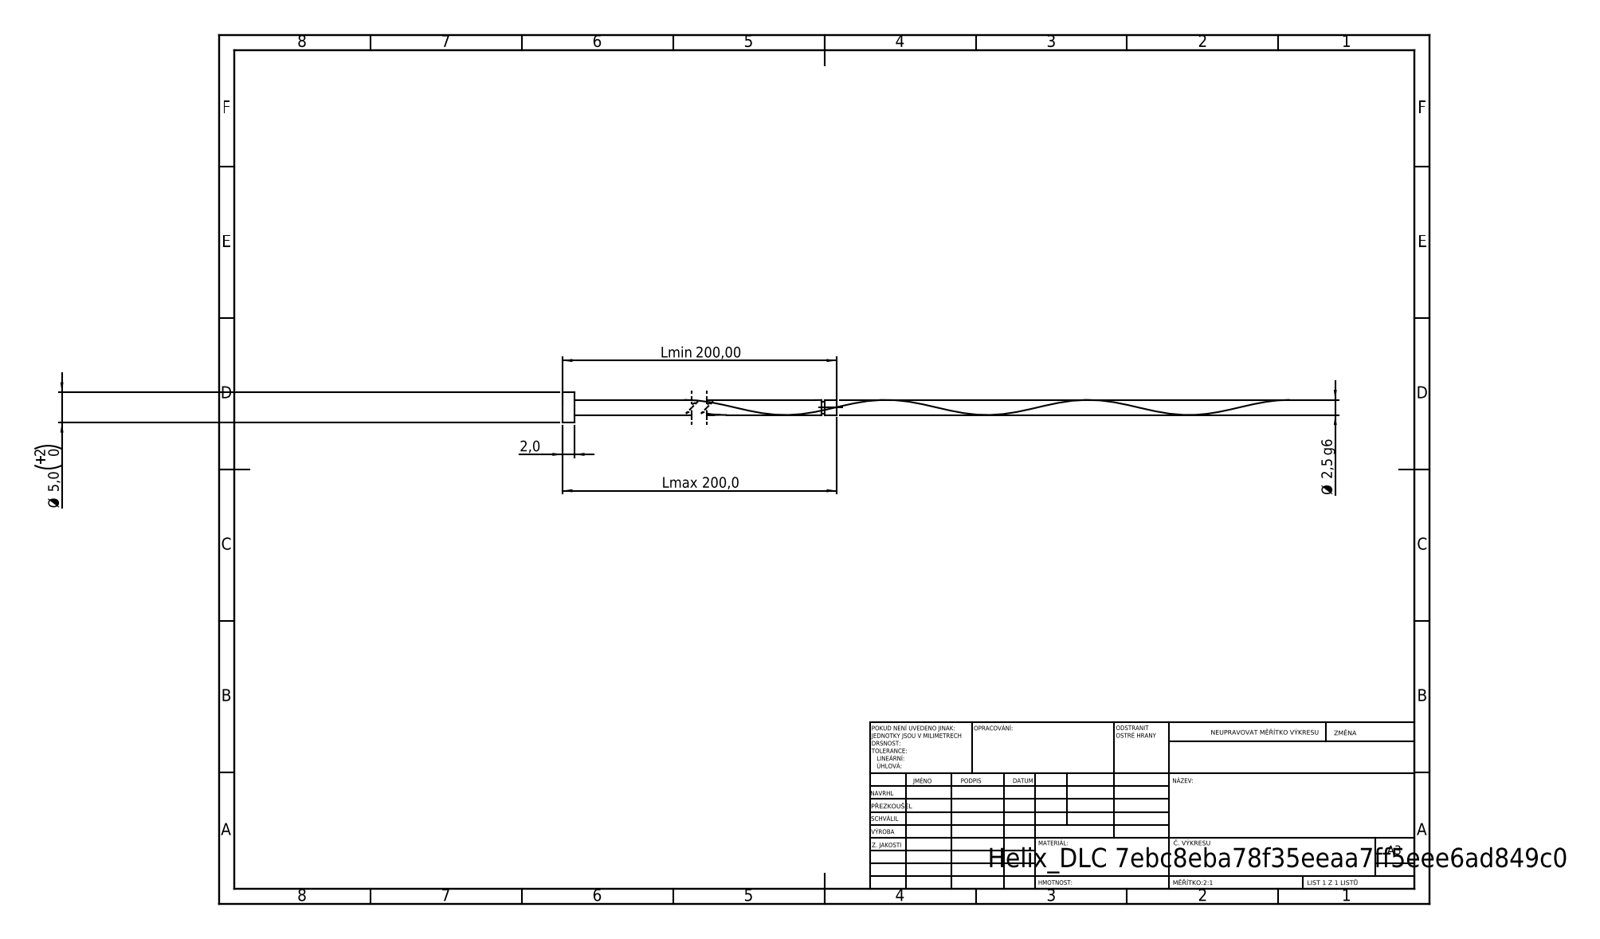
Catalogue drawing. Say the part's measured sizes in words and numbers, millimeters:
Its 3-D file was written by "SolidWorks 2019 (CONFIG_CONTROL_DESIGN)". It is 1 solid with 16 faces: 6 planar, 9 cylindrical and 1 other. Overall it measures 200 by 5 by 5 millimeters. Its volume is 1 219 cubic millimeters and its surface area 2 177 square millimeters. Round bosses or shafts: 1 of diameter 5, 1 of diameter 2.5, 1 of diameter 2. The main face-to-face distances are 2, 200, 198, 197.98, 195.98, 2.02, 197.48, 195.48, 0.5, 2.52.
